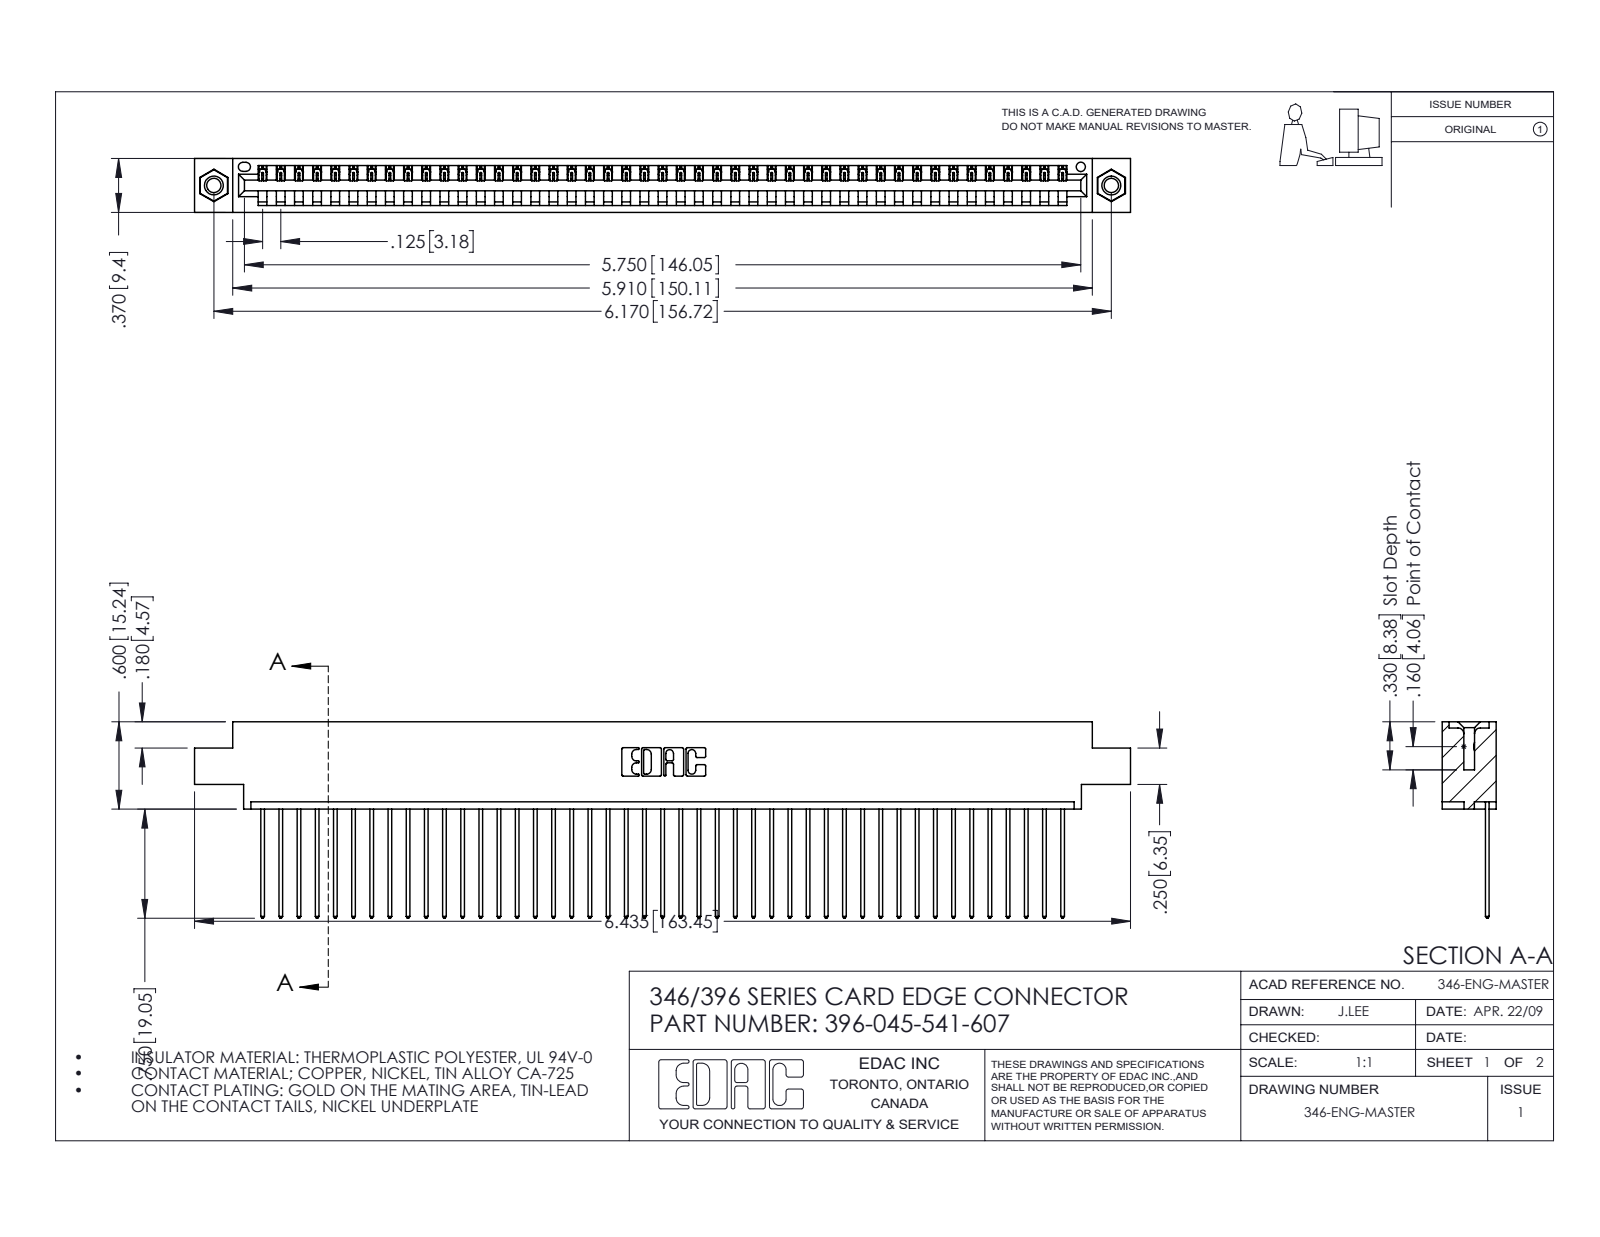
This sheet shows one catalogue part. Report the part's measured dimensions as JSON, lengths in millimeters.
{"part_name": "345-250-001_345-250-005-103; 345-292-001_345-293-141; 396-045-541-607; 346 Part_0.170 Offset - 0.156 Dia-TI", "step_written_by": "SolidWorks 2016 (CONFIG_CONTROL_DESIGN)", "units": "millimeters", "bodies": {"solids": 48, "faces": 2796, "planar": 1912, "cylindrical": 868, "other": 16}, "overall_size": [163.4, 34.3, 9.4], "volume_mm3": 15600, "surface_area_mm2": 20670, "round_holes": [[2.5, 2], [3.2, 2], [4, 2], [1.6, 1]], "round_bosses_or_shafts": [[3.9, 2]], "partial_cylinders_radius": [[0.2, 90], [0.3, 90], [0.3, 22], [0.2, 6], [0.8, 6], [0.7, 3], [0.8, 2], [1, 2]], "face_to_face_distances": [1.2, 8.2, 9.4, 6.4, 1.8, 7.6, 0.6, 5.6, 3.8, 2.5], "hole_center_spacings": [6.2, 151.4, 156.7]}
